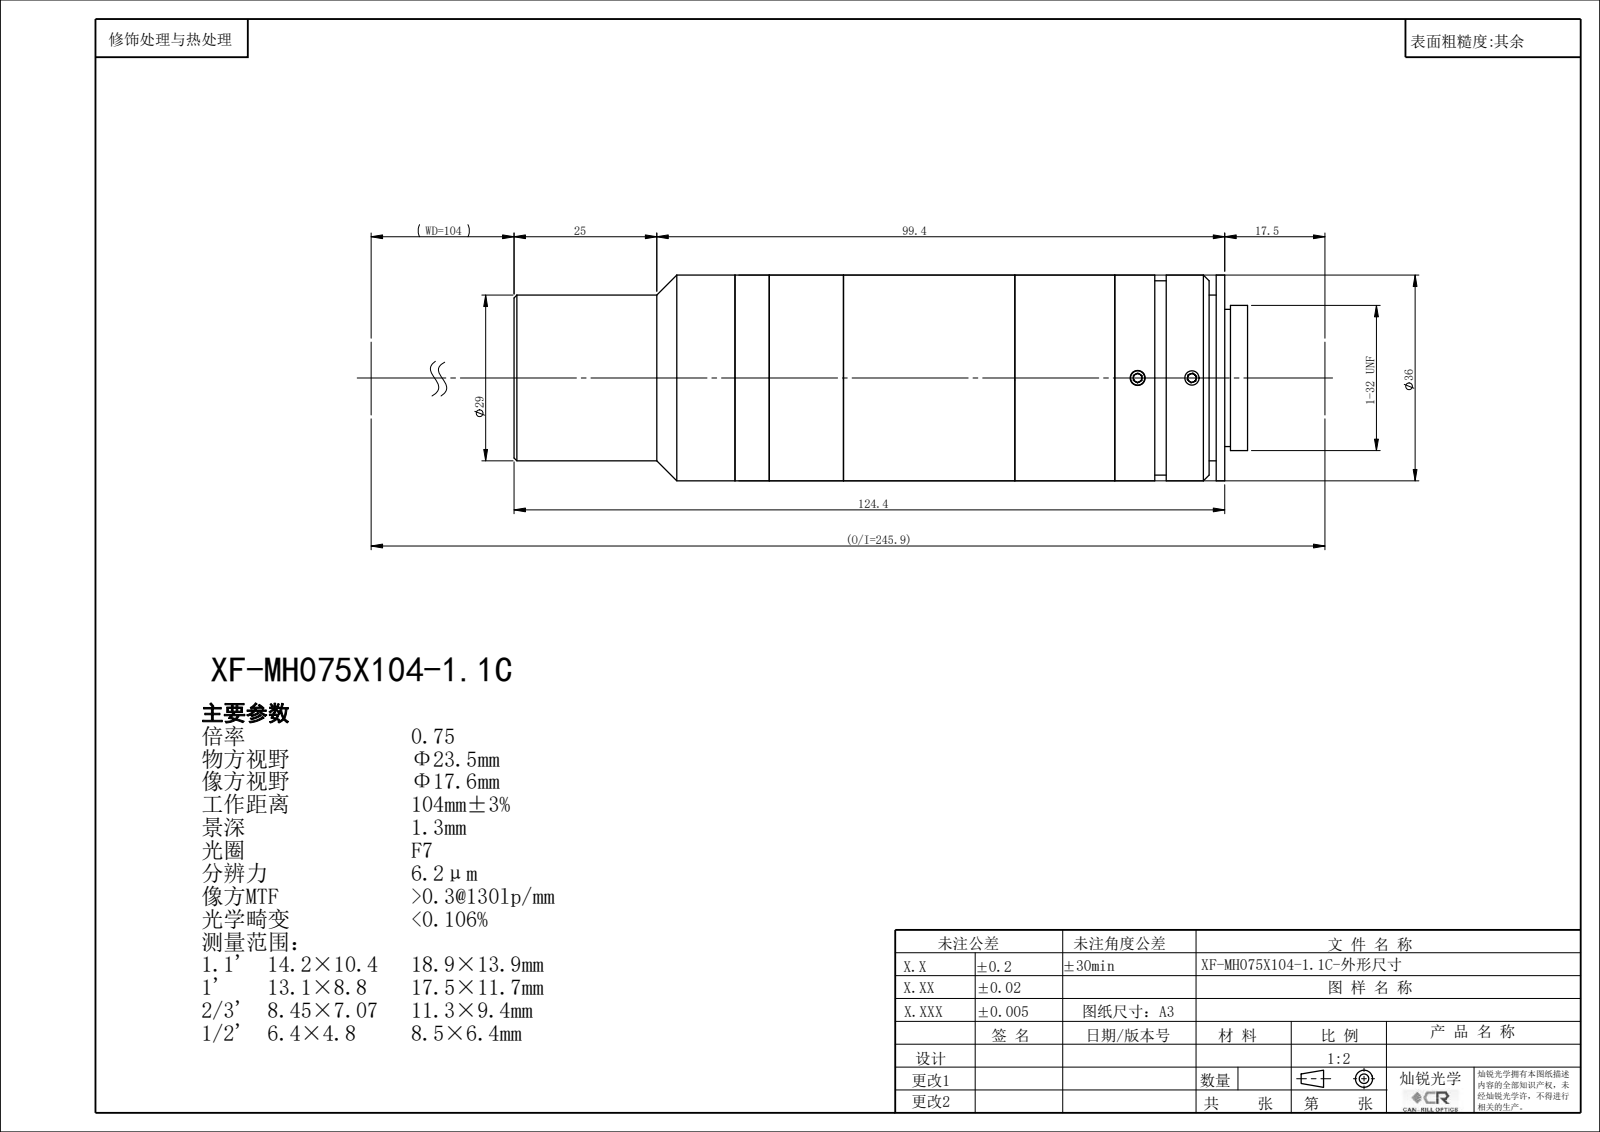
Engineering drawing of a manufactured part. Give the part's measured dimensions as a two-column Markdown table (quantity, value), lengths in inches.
| quantity | value |
| --- | --- |
| part name | XF-MH075X104-1.1C |
| STEP written by | SolidWorks 2022 (CONFIG_CONTROL_DESIGN) |
| units | inches |
| bodies | 0 solids, 141 faces (69 planar, 44 cylindrical, 28 other) |
| overall size | 5.056 × 1.417 × 1.417 |
| round holes (diameter × count) | 0.098 × 3, 0.787 × 1, 0.882 × 1, 0.945 × 1, 0.98 × 1, 1.024 × 1, 1.039 × 1 |
| round bosses / shafts (diameter × count) | 1.417 × 1, 1.339 × 1, 1.142 × 1, 1 × 1 |
| main face-to-face distances | 0.757, 0.059, 0.698, 0.689, 1.387, 1.446, 1.181, 1.87, 2.569, 2.628 |
